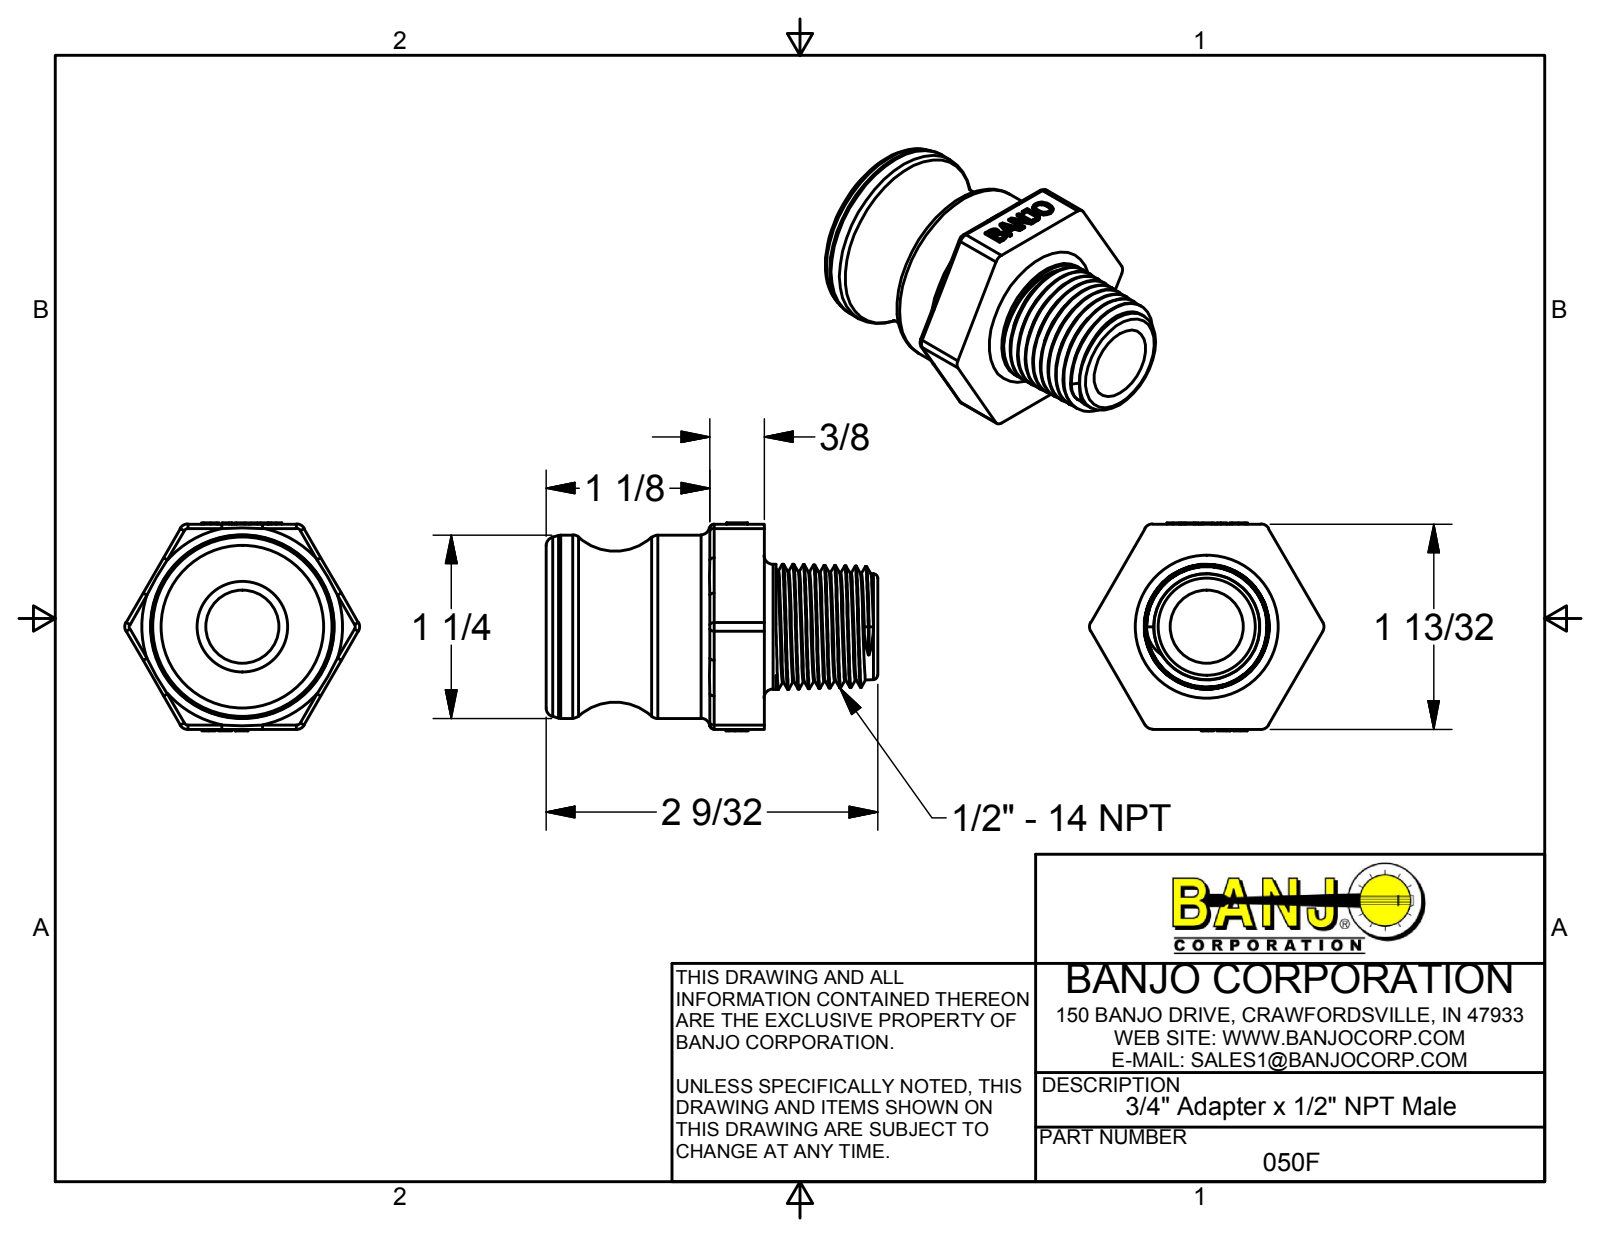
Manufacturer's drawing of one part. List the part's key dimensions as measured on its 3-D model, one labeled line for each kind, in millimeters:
Part name (STEP PRODUCT): 050F
STEP written by: Autodesk Inventor 2014 (AUTOMOTIVE_DESIGN)
Units: millimetres
Bodies: 1 solid, 213 faces (93 planar, 25 cylindrical, 95 other)
Overall size (bounding box): 57.91 × 40.91 × 36.35
Volume: 30 053 mm³ · Surface area: 10 044 mm²
Round holes (diameter × count): ⌀6.95 ×1, ⌀12.7 ×1
Round bosses / shafts (diameter × count): ⌀32 ×1, ⌀21.84 ×1
Partial cylindrical surfaces — rounded edges, fillets, slot ends (radius × count): R0.76 ×6, R1.52 ×6, R5.88 ×1
Main face-to-face distances: 35.84, 38.1, 57.91, 19.81, 28.57, 9.53, 29.34, 2.03, 40.13, 11.56
